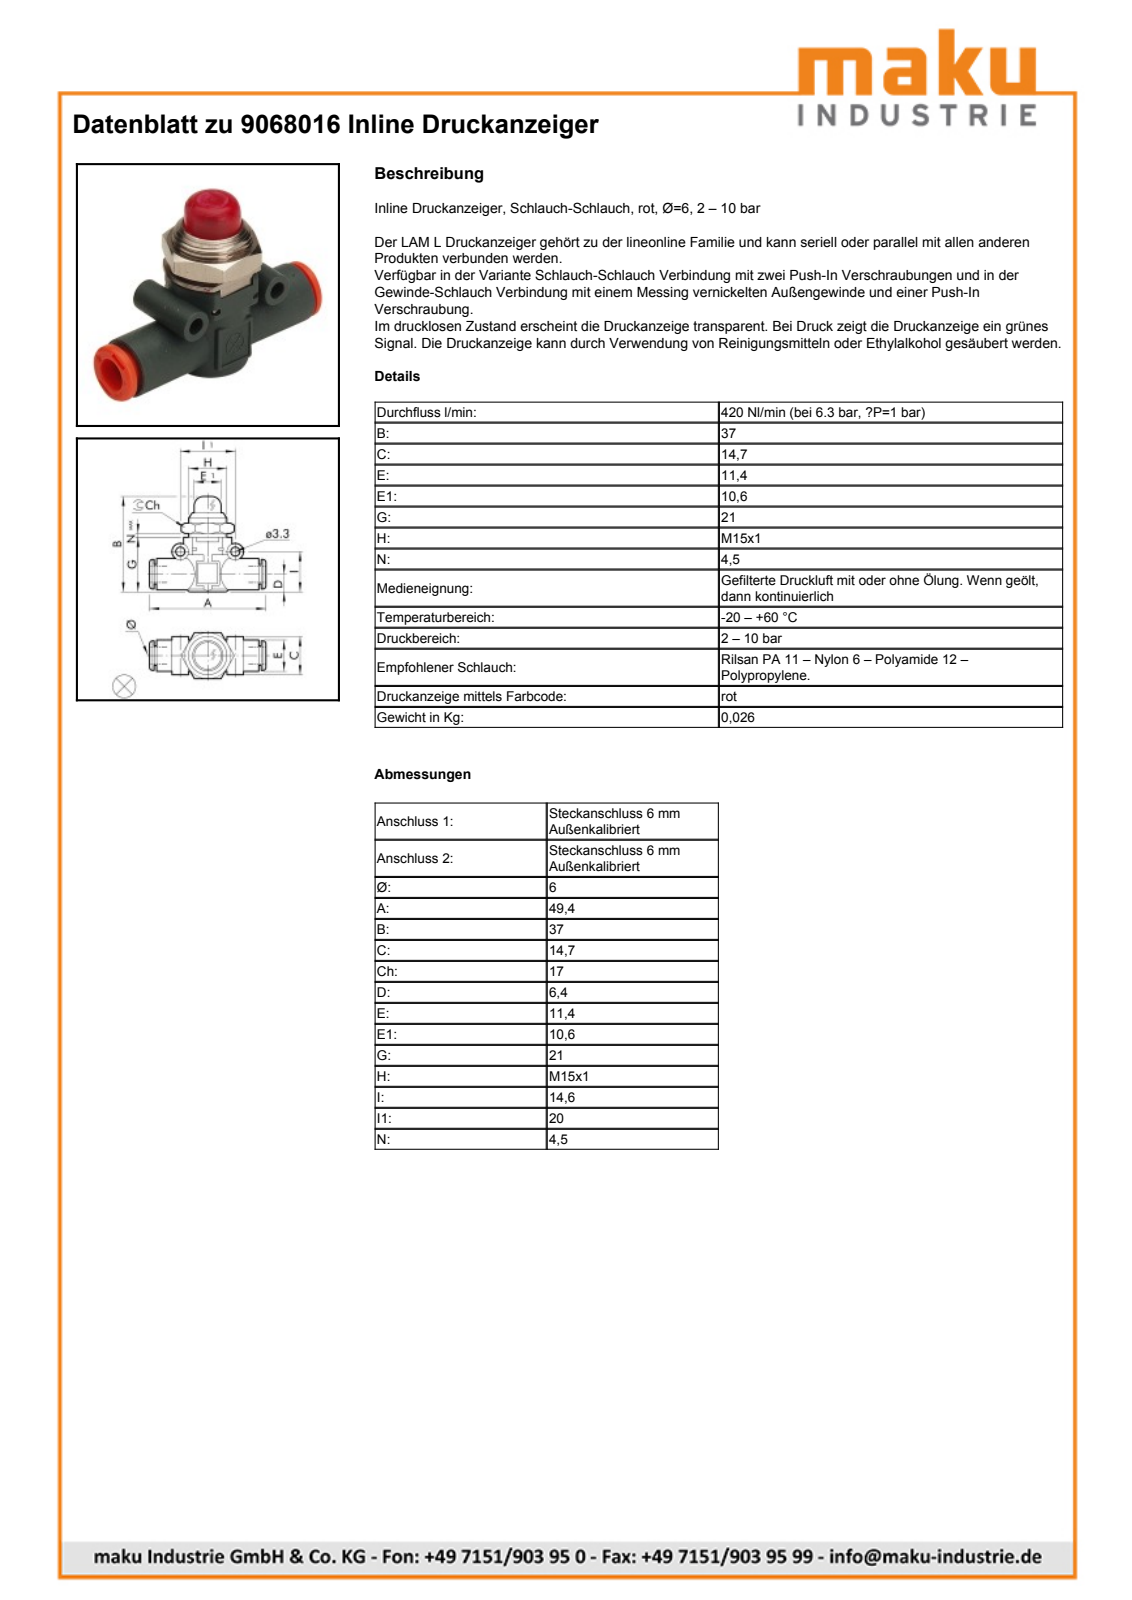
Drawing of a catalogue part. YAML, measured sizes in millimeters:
part_name: "9068016; LINE-ON-LINE D6 V2v/V3V_L body; LINE-ON-LINE D6 VNR-L bushing; LINE-ON-LINE D6 LAM-L plated"
step_written_by: "PARTsolutions (AUTOMOTIVE_DESIGN)"
units: millimeters
bodies: {solids: 4, faces: 188, planar: 104, cylindrical: 58, other: 26}
overall_size: [49.4, 37, 17]
volume: 6556
surface_area: 7195
round_holes:
  - {diameter: 3.3, count: 2}
  - {diameter: 3.5, count: 1}
  - {diameter: 4, count: 1}
  - {diameter: 6, count: 1}
  - {diameter: 6.2, count: 1}
  - {diameter: 9, count: 1}
  - {diameter: 9.6, count: 1}
  - {diameter: 10.3, count: 1}
  - {diameter: 11.6, count: 1}
round_bosses_or_shafts:
  - {diameter: 6, count: 2}
  - {diameter: 14.8, count: 1}
  - {diameter: 14, count: 1}
  - {diameter: 11.4, count: 1}
  - {diameter: 11, count: 1}
  - {diameter: 10.6, count: 1}
  - {diameter: 7.6, count: 1}
  - {diameter: 7.2, count: 1}
partial_cylinders:
  - {radius: 3.75, count: 1}
  - {radius: 7.5, count: 1}
  - {radius: 7.9, count: 1}
  - {radius: 7.95, count: 1}
  - {radius: 9.1, count: 1}
  - {radius: 9.15, count: 1}
  - {radius: 9.65, count: 1}
face_to_face_distances: [17, 1.8, 18.4, 14.1, 9.3, 16.75, 14.25, 1.4, 3.5, 2.8]
hole_center_spacings: [12.74, 20]
